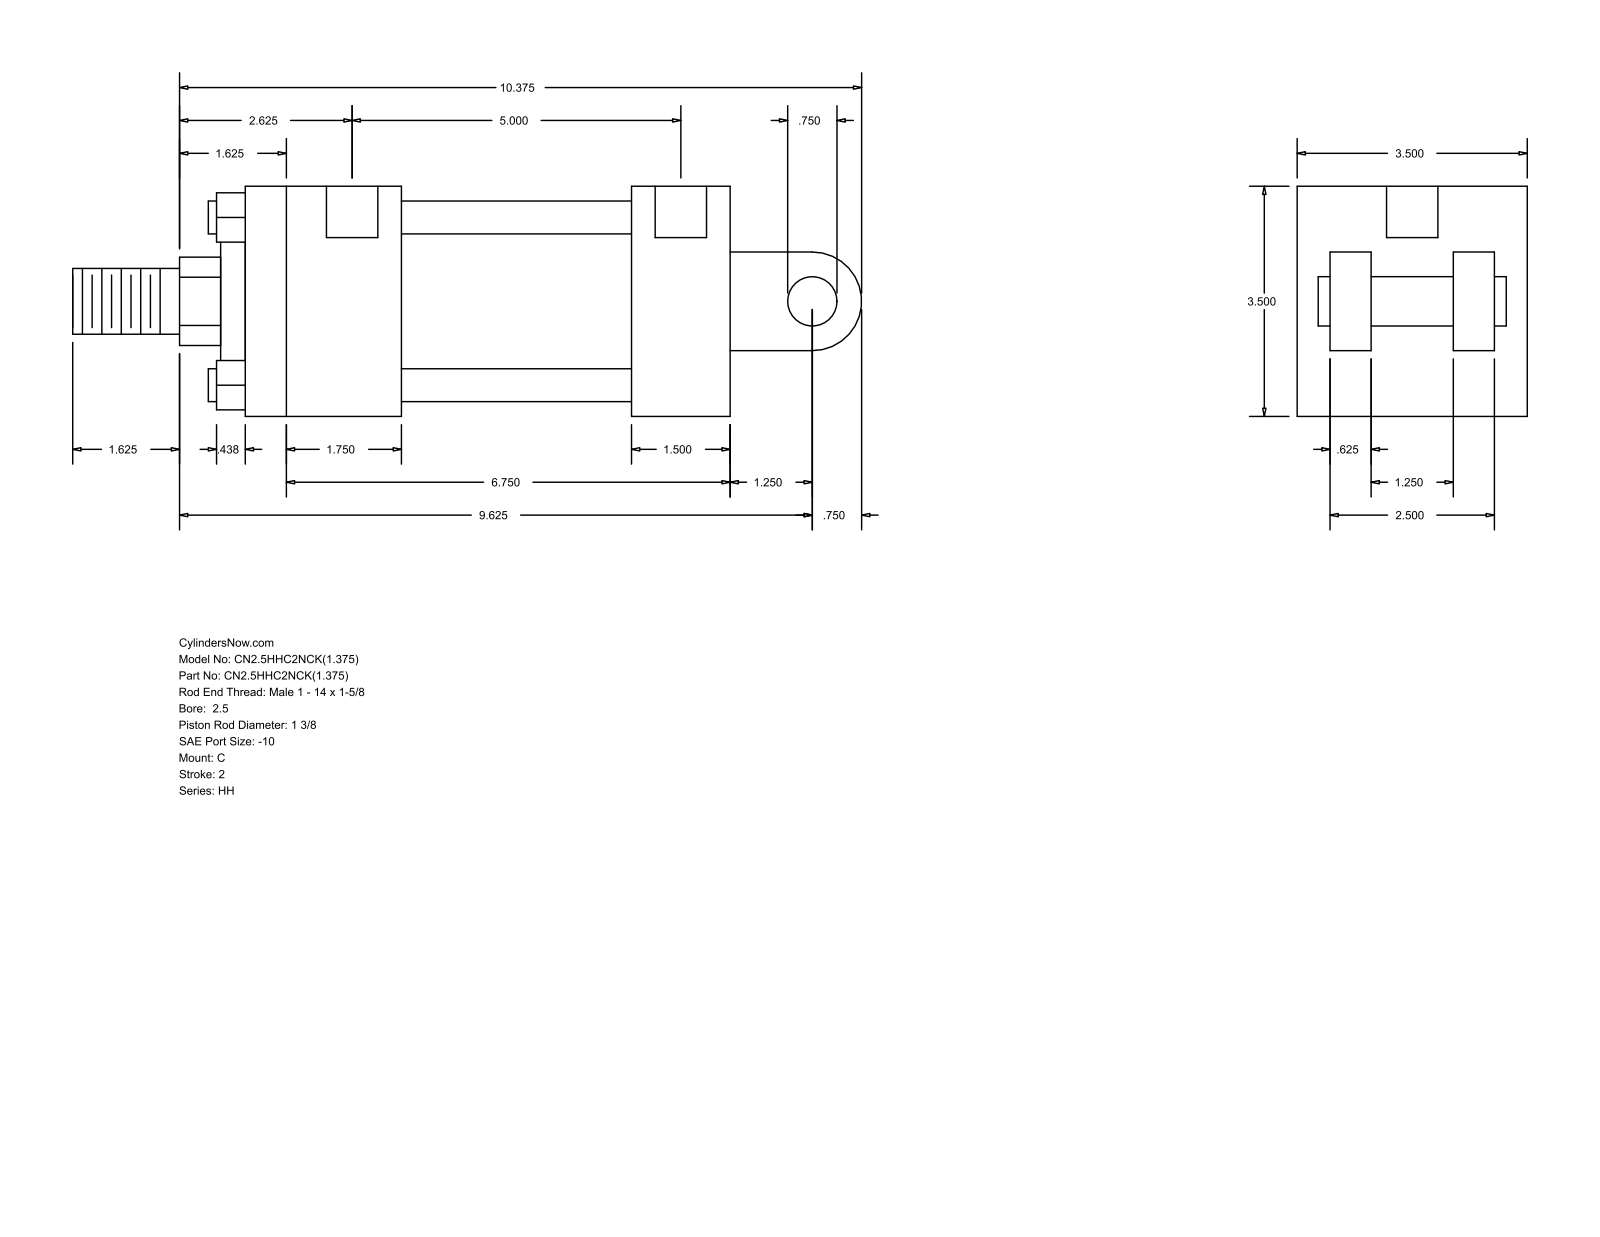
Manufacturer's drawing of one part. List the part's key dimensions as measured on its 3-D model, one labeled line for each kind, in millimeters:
Part name (STEP PRODUCT): HH_C__0250_1.375
STEP written by: GSSL Pune (CONFIG_CONTROL_DESIGN)
Units: millimetres
Bodies: 0 solids, 99 faces (70 planar, 29 cylindrical, 0 other)
Overall size (bounding box): 304.8 × 88.9 × 88.9
Round holes (diameter × count): ⌀5.56 ×4, ⌀19.84 ×2
Round bosses / shafts (diameter × count): ⌀12.7 ×4, ⌀73.03 ×1, ⌀50.8 ×1, ⌀34.92 ×1, ⌀25.4 ×1, ⌀19.05 ×1
Partial cylindrical surfaces — rounded edges, fillets, slot ends (radius × count): R17.06 ×1, R19.05 ×1
Main face-to-face distances: 88.9, 187.32, 38.1, 63.5, 12.7, 149.22, 60.32, 127, 76.2, 28.57
Hole centre spacings: 1.58, 128.59, 130.17, 127.01
